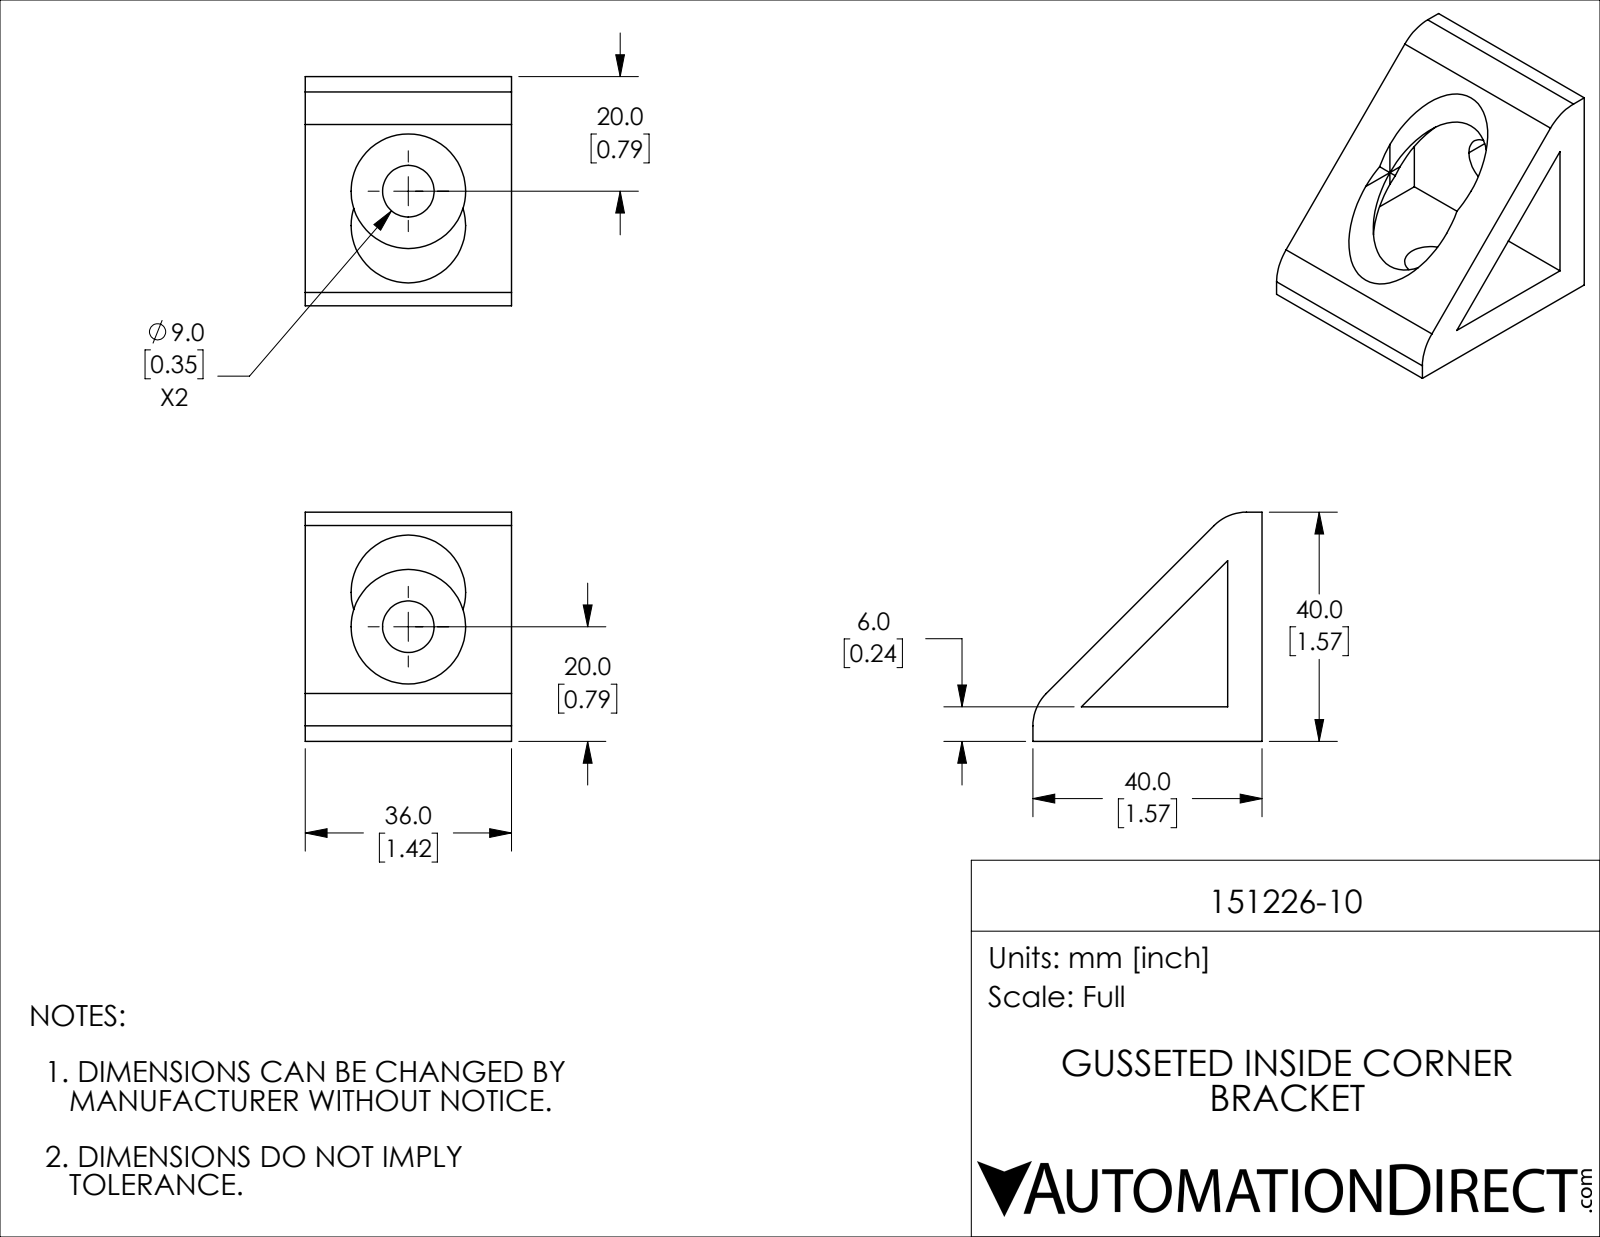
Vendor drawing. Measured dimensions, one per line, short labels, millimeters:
name: 151226-10
written by: SolidWorks 2024 (CONFIG_CONTROL_DESIGN)
unit: mm
bodies: 1 solid, 28 faces (10 planar, 18 cylindrical, 0 other)
size: 40 × 40 × 36
volume: 21 127 mm³; area: 9 077 mm²
holes: 2× ⌀9, 2× ⌀20
rounds: 2× R8
face distances: 6, 36, 40, 34
